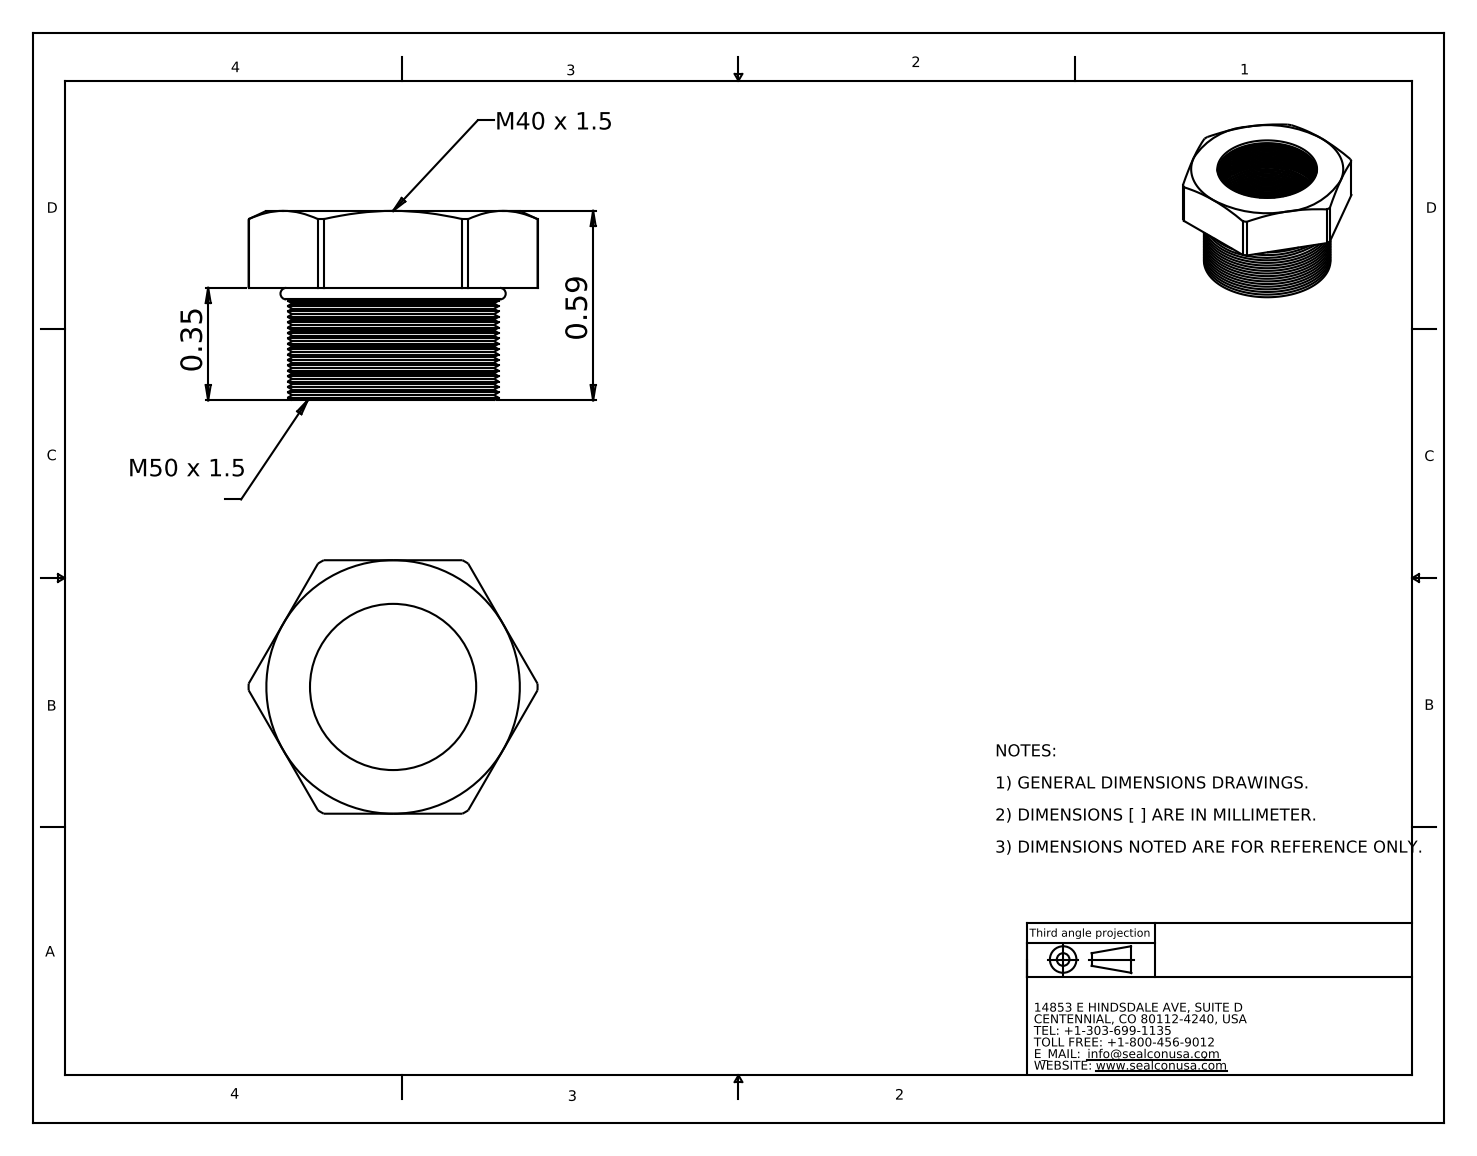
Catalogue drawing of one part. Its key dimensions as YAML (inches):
part_name: "RM-5040-SS-B"
step_written_by: "SolidWorks 2008 (CONFIG_CONTROL_DESIGN)"
units: inches
bodies: {solids: 2, faces: 361, planar: 9, cylindrical: 121, other: 231}
overall_size: [0.901, 0.79, 0.59]
volume: 0.118
surface_area: 4.79
round_holes:
  - {diameter: 0.518, count: 1}
round_bosses_or_shafts:
  - {diameter: 0.63, count: 1}
partial_cylinders:
  - {radius: 0.45, count: 1}
face_to_face_distances: [0.79, 0.24, 0.35, 0.59]
